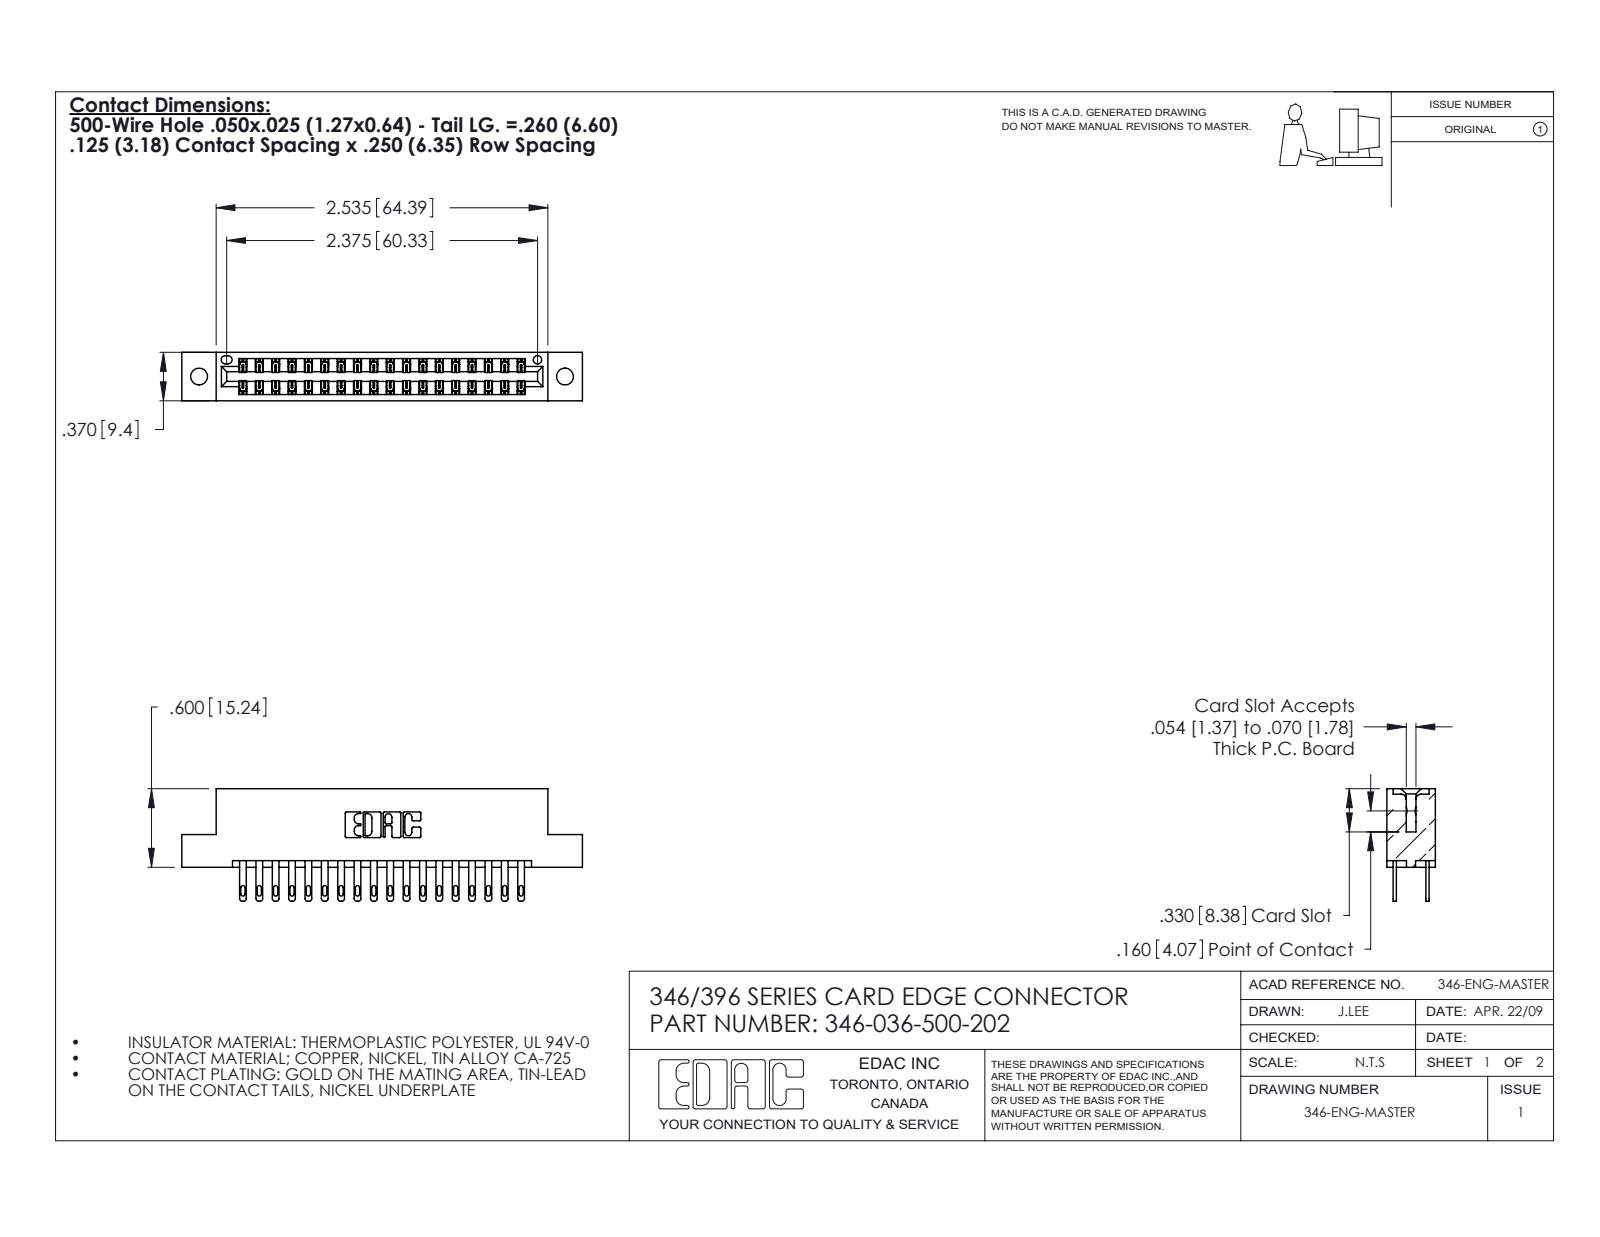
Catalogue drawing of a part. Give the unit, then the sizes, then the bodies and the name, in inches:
Units: inches
Overall size (bounding box): 3.06 × 0.86 × 0.37
Round holes (diameter × count): ⌀0.128 ×2, ⌀0.064 ×1
Partial cylindrical surfaces — rounded edges, fillets, slot ends (radius × count): R0.006 ×54, R0.016 ×36, R0.02 ×36, R0.01 ×22, R0.007 ×6, R0.031 ×6, R0.026 ×3, R0.014 ×2
Main face-to-face distances: 0.048, 0.322, 0.25, 0.37, 0.072, 0.298, 0.025, 0.275, 0.148, 0.222
Hole centre spacings: 0.246, 2.588, 2.795
Volume: 0.456 in³ · Surface area: 15.49 in²
Bodies: 37 solids, 1850 faces (1120 planar, 730 cylindrical, 0 other)
Part name (STEP PRODUCT): 346 Part_Flush Mounting Lugs - 0.128 Dia; 345-292-001_345-293-100; 346-036-500-202
STEP written by: SolidWorks 2020 (CONFIG_CONTROL_DESIGN)
